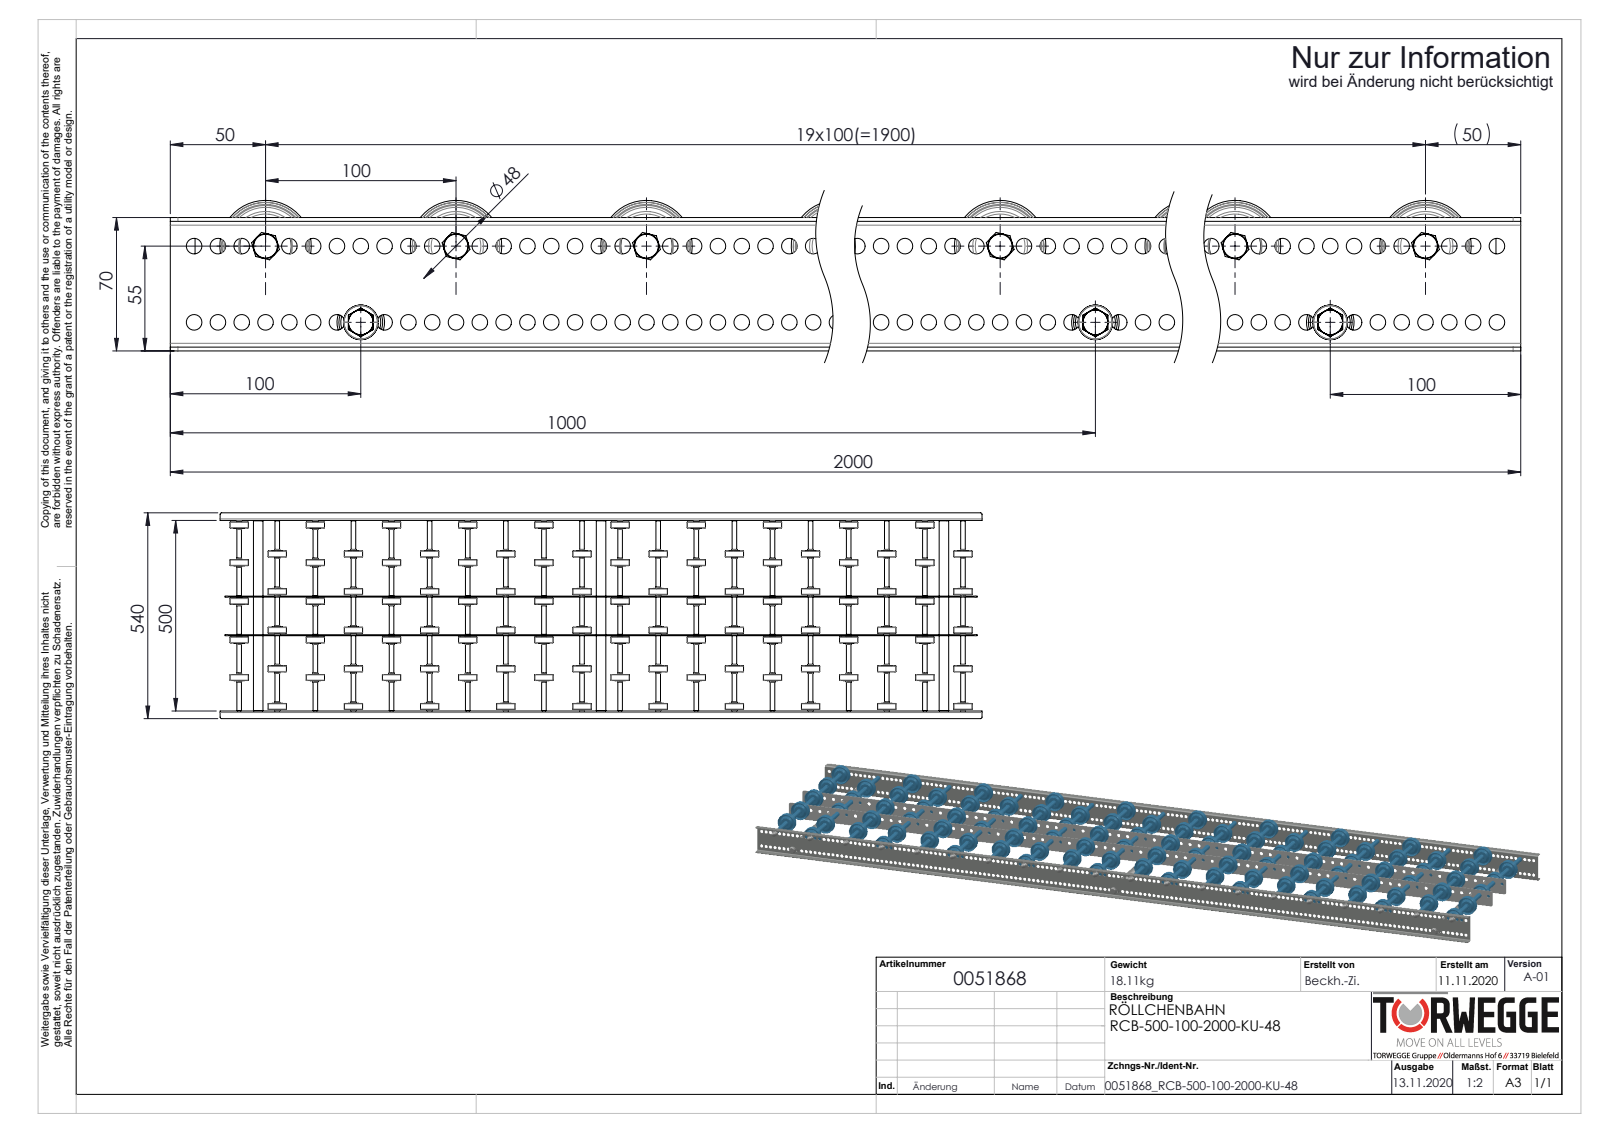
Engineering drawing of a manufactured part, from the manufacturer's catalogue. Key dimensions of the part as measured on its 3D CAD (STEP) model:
Part name (STEP PRODUCT): S106837_Gewindestange-M8-KFG_L520; Profil_LRB-20x70x20x2_KFG_S100202_U-PROFIL-20-70-20-2-LRB-L=2000; S100100_Längstraverse-42x2,5_S100103_Lngstraverse-RB-L2000; S100994_Sperrzahnschraube_M08x16-8.8-A2K (+6 more)
STEP written by: SolidWorks 2020 (AUTOMOTIVE_DESIGN)
Units: millimetres
Bodies: 279 solids, 10782 faces (1834 planar, 4072 cylindrical, 4876 other)
Overall size (bounding box): 2000 × 540 × 79
Volume: 4 175 000 mm³ · Surface area: 3 166 000 mm²
Round holes (diameter × count): ⌀8.2 ×318, ⌀8.5 ×79, ⌀6.65 ×20, ⌀9.65 ×20, ⌀13.7 ×20, ⌀6.8 ×3, ⌀21 ×3
Round bosses / shafts (diameter × count): ⌀8 ×23, ⌀48 ×20, ⌀27 ×20, ⌀12.7 ×20, ⌀12.5 ×20, ⌀12 ×20, ⌀25 ×3
Partial cylindrical surfaces — rounded edges, fillets, slot ends (radius × count): R4 ×8, R2 ×4, R5 ×4
Main face-to-face distances: 2, 502, 101.3, 2.5, 68, 504, 500, 200.1, 301.4, 98.8
Hole centre spacings: 12.5, 25, 37.5, 50, 62.5, 75, 87.5, 100
